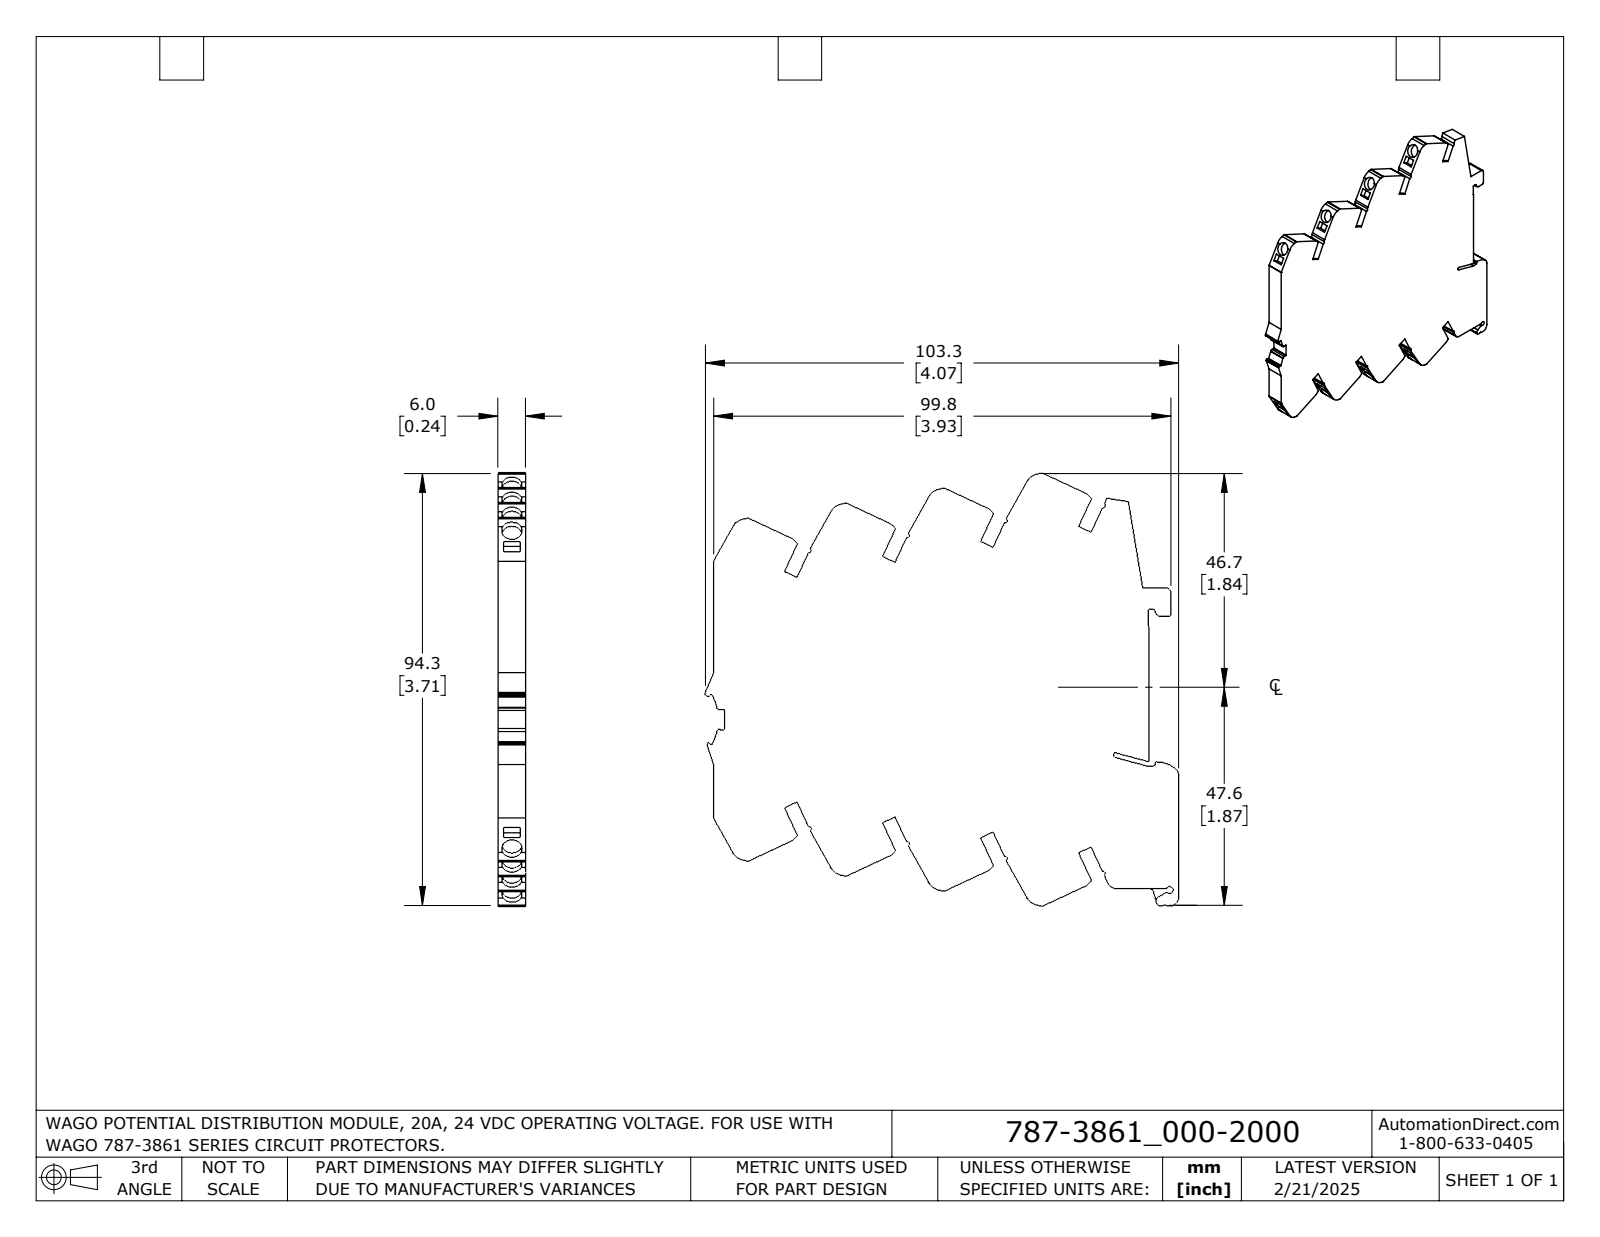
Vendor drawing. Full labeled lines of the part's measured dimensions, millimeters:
Part name (STEP PRODUCT): 787-3861_000-2000_HI
STEP written by: SolidWorks 2024 (AUTOMOTIVE_DESIGN)
Units: millimetres
Bodies: 1 solid, 255 faces (191 planar, 64 cylindrical, 0 other)
Overall size (bounding box): 103.3 × 94.26 × 6
Volume: 44 000 mm³ · Surface area: 18 850 mm²
Round holes (diameter × count): ⌀4.4 ×8
Partial cylindrical surfaces — rounded edges, fillets, slot ends (radius × count): R0.2 ×13, R0.5 ×12, R0.4 ×8, R3.35 ×8, R1 ×5, R0.3 ×3, R2 ×3, R0.45 ×2
Main face-to-face distances: 6, 17.99, 17.02, 35.98, 3, 12.01, 20.99, 12, 34.04, 38.98
Hole centre spacings: 13.35, 13.34, 26.7, 26.71, 40.05
